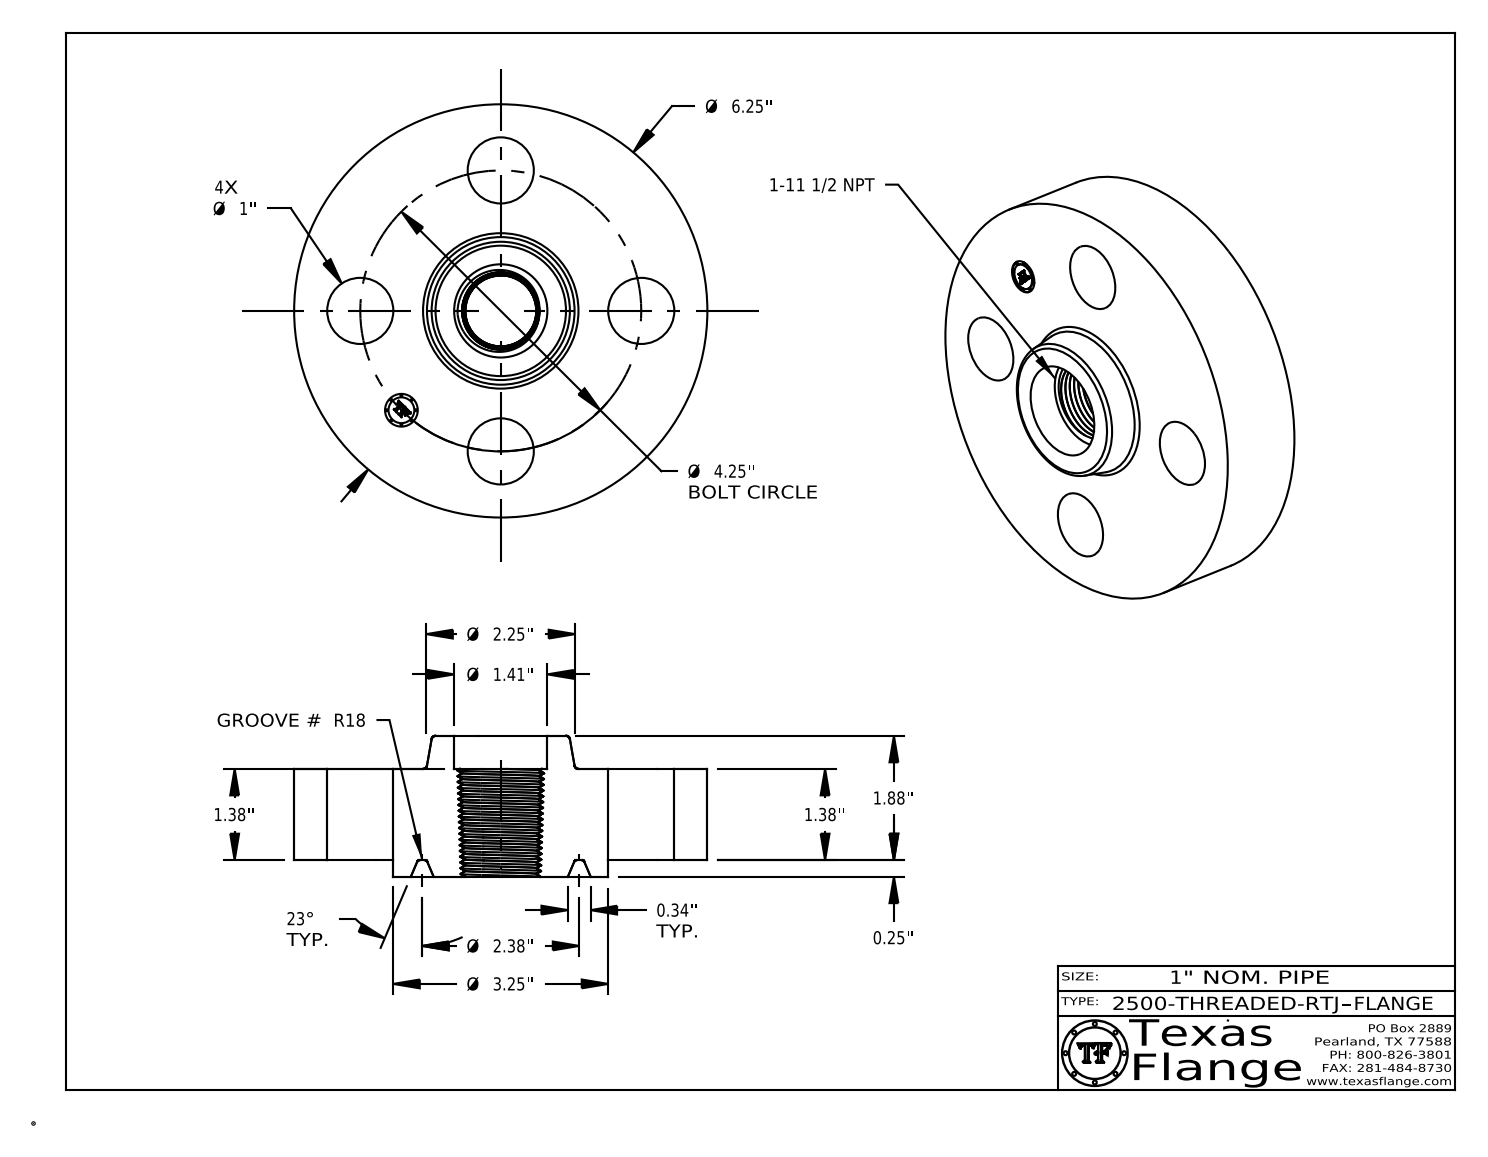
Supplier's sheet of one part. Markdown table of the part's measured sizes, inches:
| quantity | value |
| --- | --- |
| part name | 2500-THREADED-RTJ |
| STEP written by | CATIA V5 STEP AP214 (AUTOMOTIVE_DESIGN) |
| units | inches |
| bodies | 1 solid, 613 faces (372 planar, 34 cylindrical, 207 other) |
| overall size | 6.25 × 6.25 × 2.13 |
| volume | 38.88 in³ |
| surface area | 118.6 in² |
| round holes (diameter × count) | 1 × 4, 0.495 × 1, 1.41 × 1 |
| round bosses / shafts (diameter × count) | 0.03 × 8, 6.25 × 1, 3.25 × 1, 0.39 × 1 |
| main face-to-face distances | 1.38, 0.25, 1.63, 2.13, 1.88, 0.5, 1.615, 1.365, 0.015, 0.515 |
| hole center spacings | 2.125, 3.006, 1.626, 3.927, 4.25 |
